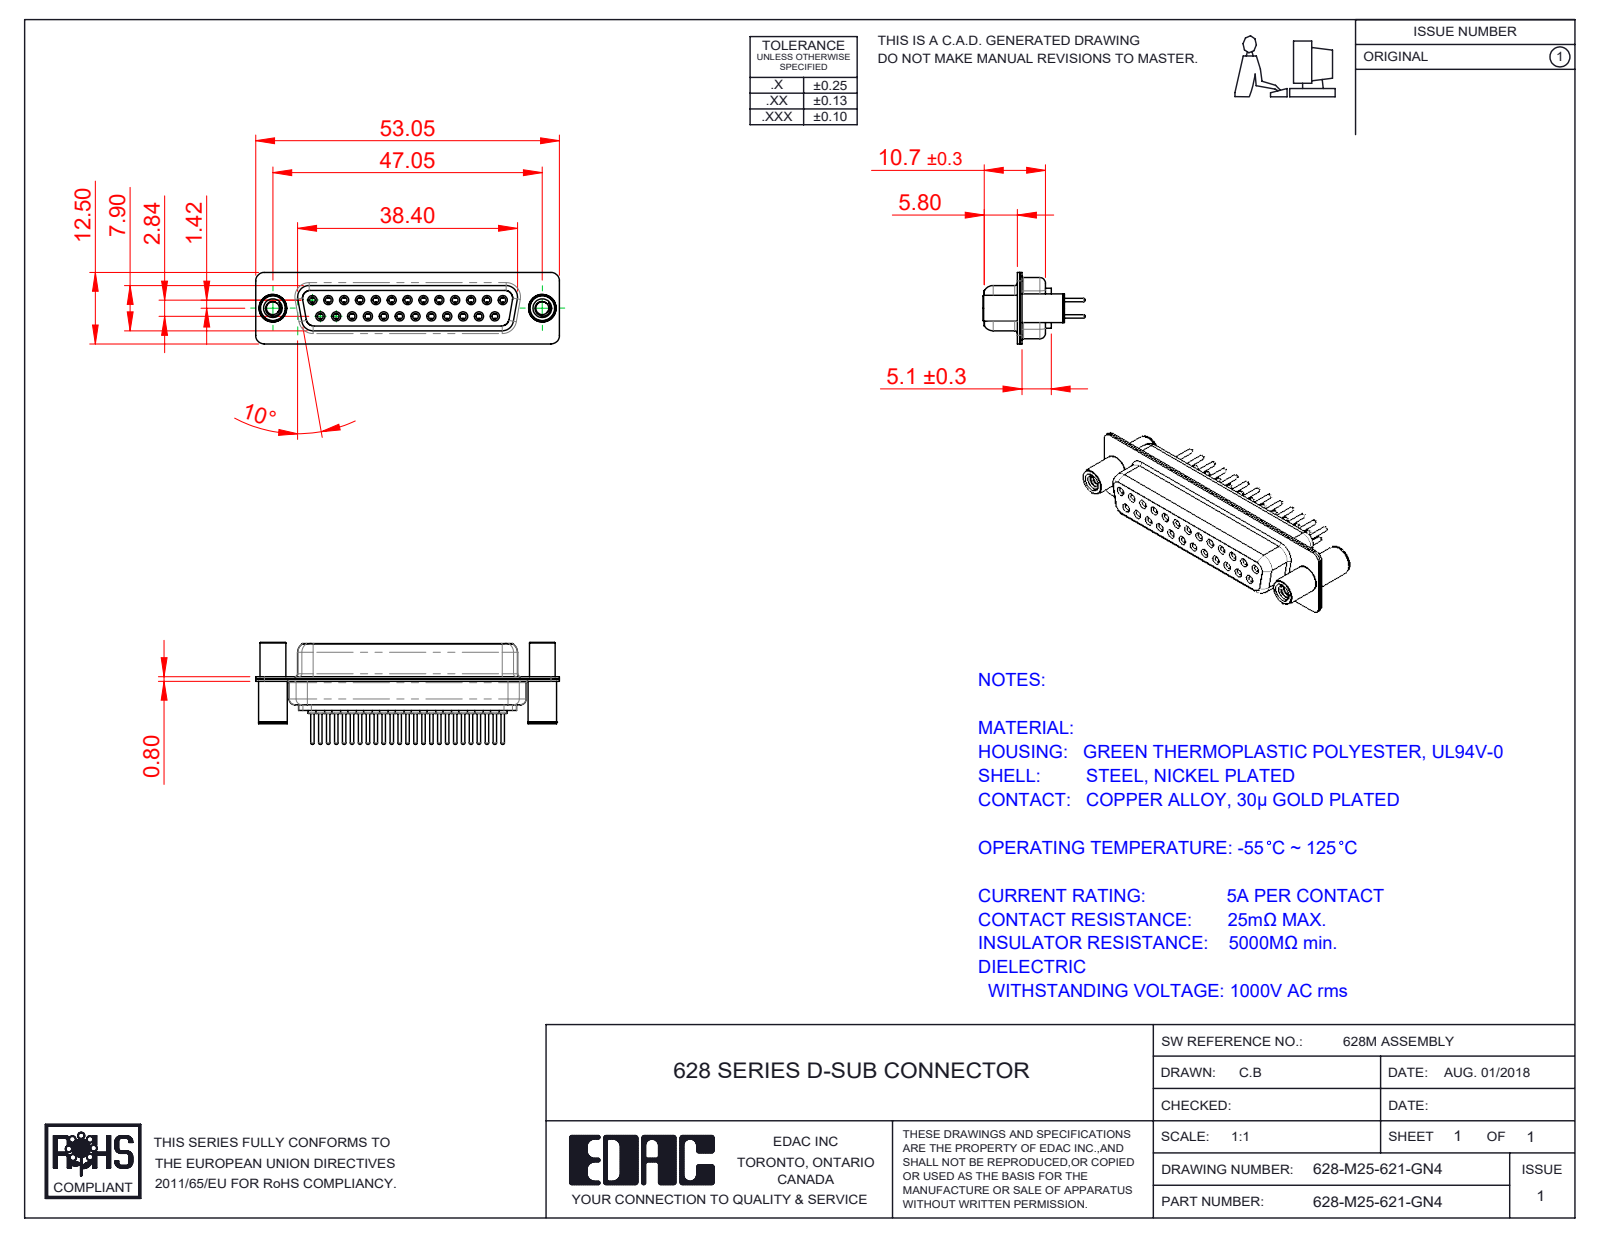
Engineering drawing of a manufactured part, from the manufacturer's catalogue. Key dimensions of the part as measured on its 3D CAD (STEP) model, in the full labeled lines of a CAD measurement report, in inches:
Part name (STEP PRODUCT): 628M Shell Front_25 Contacts; 628M Shell Rear_25 Contacts; 628M Contact Row 2_21; 628M 4-40 Threaded Standoff and Board Spacer (+3 more)
STEP written by: SolidWorks 2020 (CONFIG_CONTROL_DESIGN)
Units: inches
Bodies: 30 solids, 1740 faces (448 planar, 664 cylindrical, 628 other)
Overall size (bounding box): 2.089 × 0.701 × 0.492
Volume: 0.246 in³ · Surface area: 15 in²
Round holes (diameter × count): ⌀0.039 ×25, ⌀0.043 ×25, ⌀0.067 ×25, ⌀0.071 ×25, ⌀0.079 ×25, ⌀0.089 ×2, ⌀0.128 ×2, ⌀0.157 ×2, ⌀0.189 ×2
Round bosses / shafts (diameter × count): ⌀0.087 ×25, ⌀0.063 ×25, ⌀0.059 ×25, ⌀0.024 ×25, ⌀0.197 ×2, ⌀0.193 ×2, ⌀0.177 ×2
Partial cylindrical surfaces — rounded edges, fillets, slot ends (radius × count): R0.059 ×16, R0.079 ×12, R0.053 ×8, R0.063 ×8, R0.01 ×4, R0.02 ×4, R0.024 ×4, R0.026 ×4
Main face-to-face distances: 0.016, 0.055, 0.018, 0.333, 0.35, 0.071, 0.244, 0.278, 0.039, 0.073
Hole centre spacings: 0.124, 0.109, 0.218, 0.327, 0.436, 0.545, 0.198, 0.295
